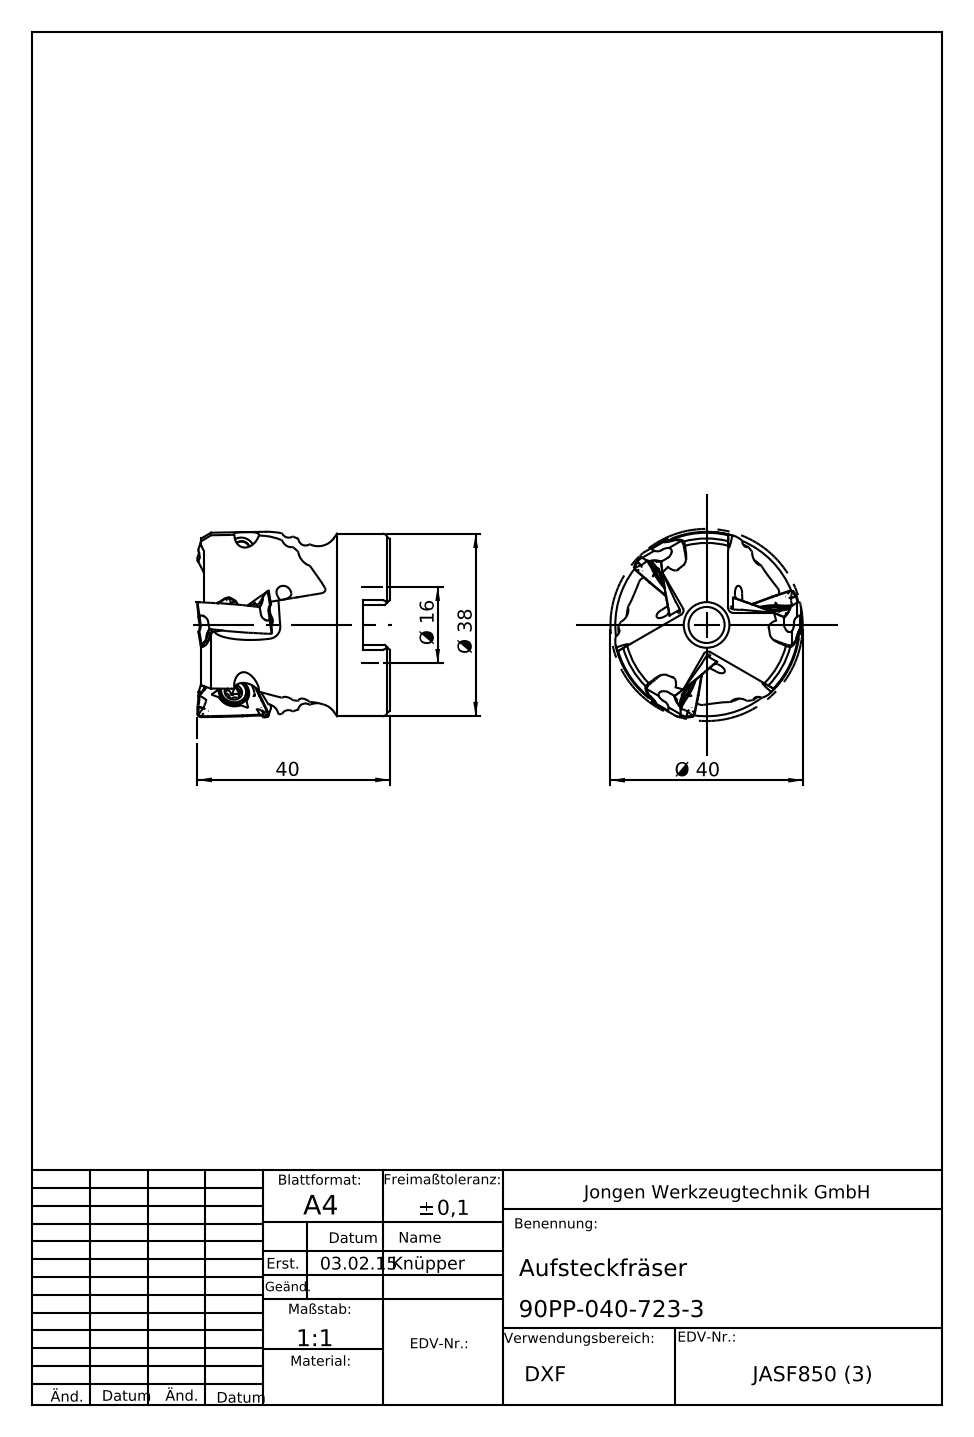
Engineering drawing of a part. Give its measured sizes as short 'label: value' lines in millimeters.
name: 90PP_040_723_3
written by: SolidWorks 2016 (AUTOMOTIVE_DESIGN)
unit: mm
bodies: 1 solid, 268 faces (76 planar, 80 cylindrical, 112 other)
size: 40.04 × 39.98 × 39.98
volume: 34 398 mm³; area: 10 667 mm²
holes: 3× ⌀3, 1× ⌀7.5, 1× ⌀16, 1× ⌀16.15, 1× ⌀16.3
bosses: 1× ⌀38
rounds: 24× R1.25, 6× R2, 6× R2.5, 3× R0.4, 3× R1, 3× R20
face distances: 38.7, 5.55, 33.15, 20, 14.45, 18.7, 8.4, 25.46, 14.95, 9.4
